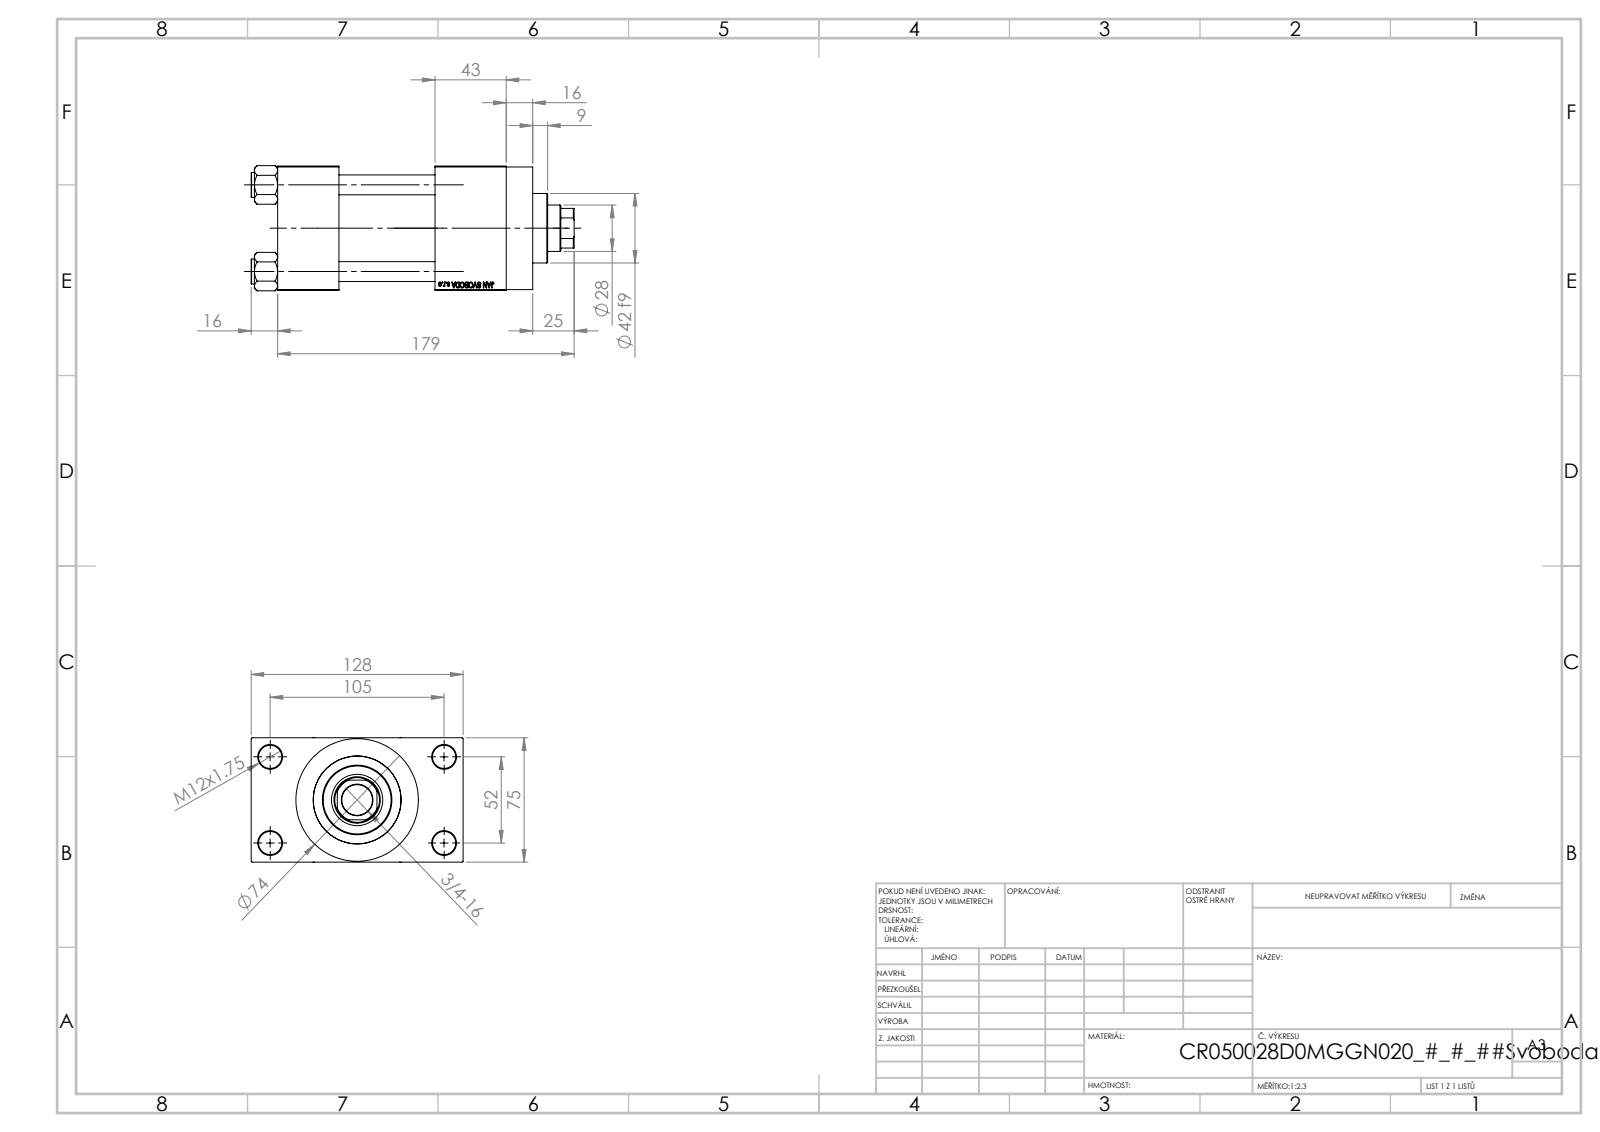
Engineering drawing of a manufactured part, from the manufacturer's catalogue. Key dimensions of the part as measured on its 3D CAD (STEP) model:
Part name (STEP PRODUCT): V215CR_VCP_D; V215CR_D_Body; NUT_M5_D; V215_VC_A (+1 more)
STEP written by: SolidWorks 2019 (CONFIG_CONTROL_DESIGN)
Units: millimetres
Bodies: 11 solids, 1104 faces (497 planar, 89 cylindrical, 518 other)
Overall size (bounding box): 195 × 128 × 75.54
Volume: 815 231 mm³ · Surface area: 168 868 mm²
Round holes (diameter × count): ⌀12 ×4, ⌀14 ×4, ⌀7 ×2, ⌀20.96 ×2, ⌀30 ×2, ⌀18.5 ×1, ⌀28 ×1, ⌀31 ×1, ⌀41 ×1, ⌀50 ×1, ⌀53 ×1
Round bosses / shafts (diameter × count): ⌀15 ×4, ⌀74 ×1, ⌀56 ×1, ⌀42 ×1
Partial cylindrical surfaces — rounded edges, fillets, slot ends (radius × count): R13.5 ×1
Main face-to-face distances: 75, 58, 37, 95, 26.5, 101.5, 138, 101, 43, 16
Hole centre spacings: 26.35, 36.98, 52.3, 58.43, 58.59, 78.65, 94.37, 52
